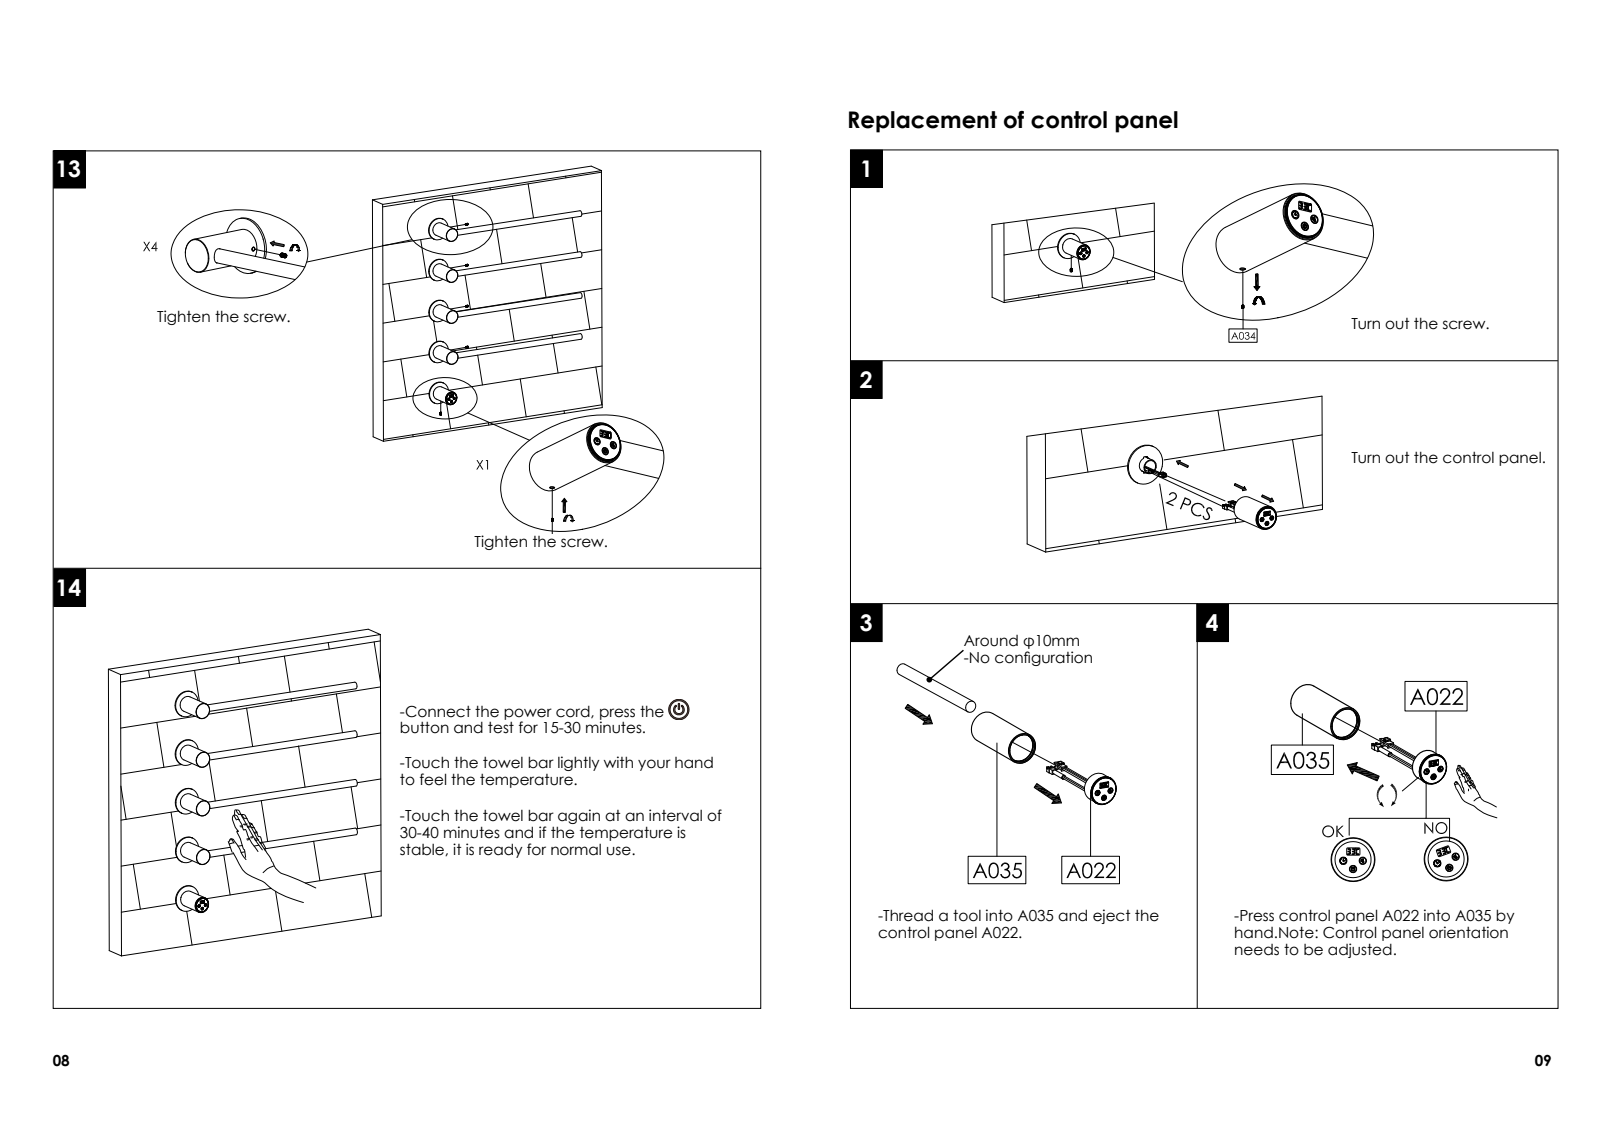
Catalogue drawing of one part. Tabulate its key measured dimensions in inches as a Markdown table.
| quantity | value |
| --- | --- |
| part name | 250002_ASM_6_1_ASM_1_ASM; 250001_ASM_12_1_ASM_1_ASM; 7835310300_7_1_1; 7835351100_4_1_1 (+8 more) |
| STEP written by | CREO PARAMETRIC BY PTC INC, 2019224 (CONFIG_CONTROL_DESIGN) |
| units | inches |
| bodies | 34 solids, 1271 faces (486 planar, 502 cylindrical, 283 other) |
| overall size | 24.016 × 20.472 × 3.465 |
| volume | 34.24 in³ |
| surface area | 581.9 in² |
| round holes (diameter × count) | 0.165 × 9, 0.63 × 8, 1.008 × 5, 0.315 × 4, 0.713 × 4, 0.748 × 4, 0.992 × 4, 0.256 × 3, 0.039 × 1, 0.988 × 1, 1.417 × 1, 1.496 × 1 |
| round bosses / shafts (diameter × count) | 0.059 × 10, 0.197 × 9, 2.756 × 5, 1.654 × 5, 0.882 × 4, 0.709 × 4, 0.433 × 4, 0.354 × 4 |
| partial cylindrical surfaces (radius × count) | 0.02 × 67, 0.008 × 40, 0.01 × 6, 0.591 × 5, 0.039 × 4, 0.189 × 4, 0.236 × 4, 0.028 × 2 |
| main face-to-face distances | 0.118, 0.039, 3.465, 3.346, 0.157, 3.307, 0.079, 3.425, 0.197, 5.315 |
| hole center spacings | 5.315, 10.63, 15.945, 5.318, 5.324, 5.338, 5.815, 5.317 |
